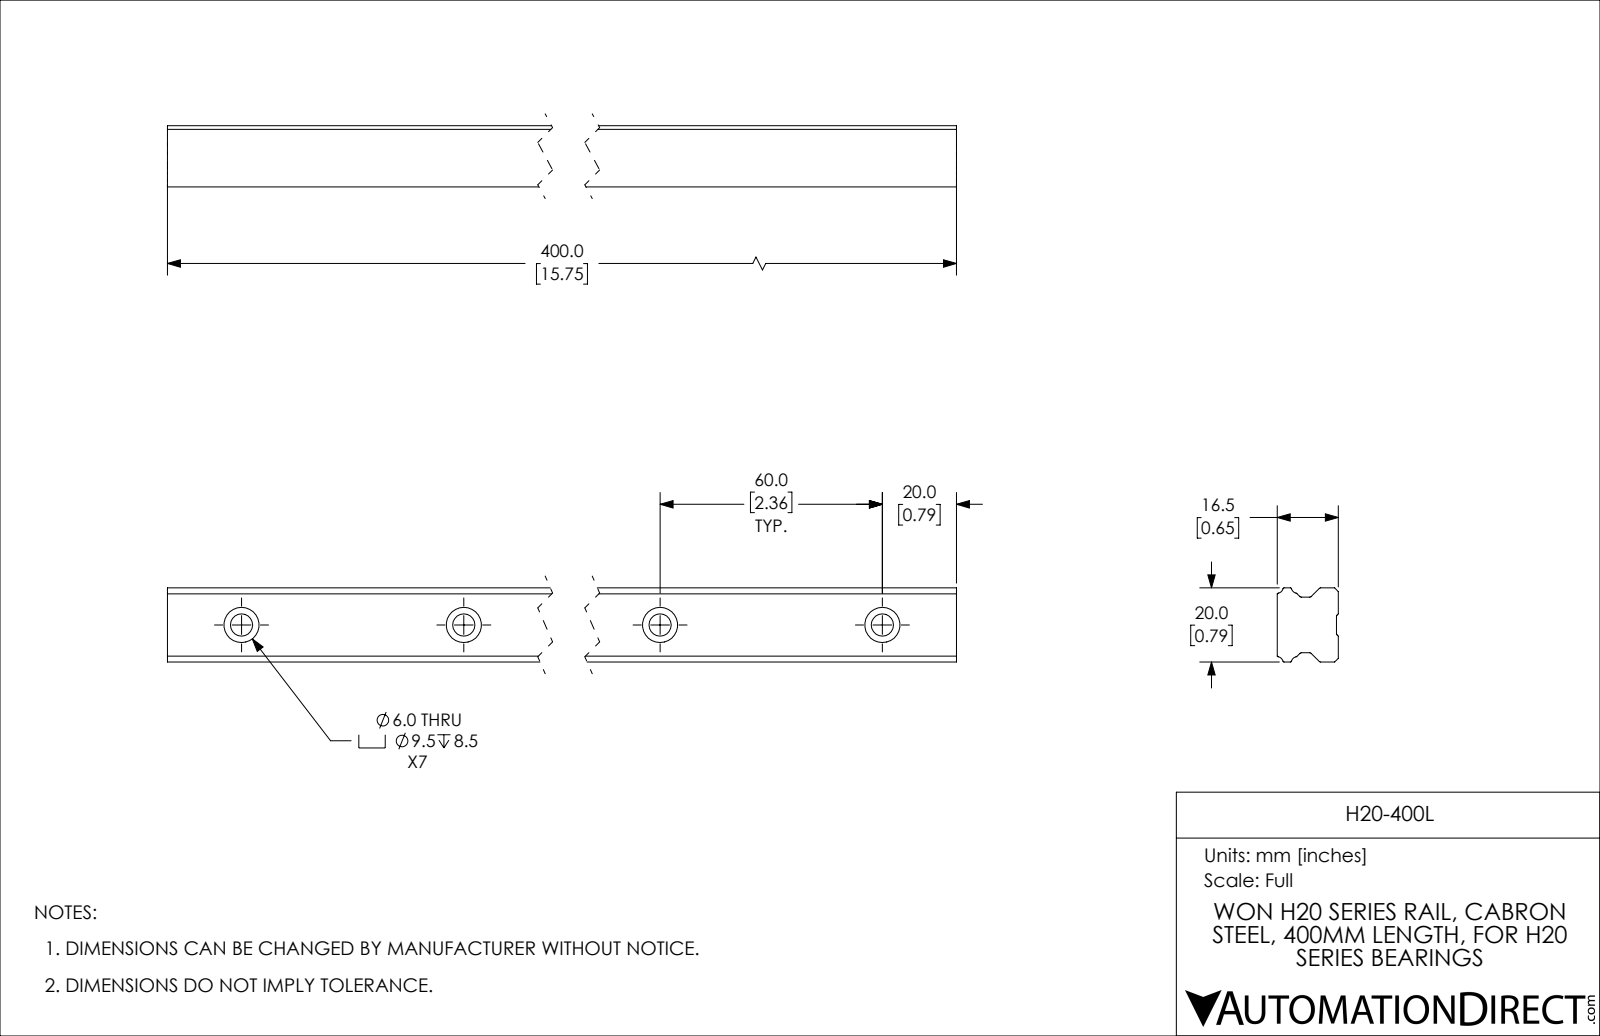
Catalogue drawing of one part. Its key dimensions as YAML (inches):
part_name: "H20-400L"
step_written_by: "SolidWorks 2019 (CONFIG_CONTROL_DESIGN)"
units: inches
bodies: {solids: 1, faces: 110, planar: 48, cylindrical: 62, other: 0}
overall_size: [15.748, 0.787, 0.65]
volume: 6.87
surface_area: 50.88
round_holes:
  - {diameter: 0.236, count: 7}
  - {diameter: 0.374, count: 7}
partial_cylinders:
  - {radius: 0.02, count: 12}
  - {radius: 0.012, count: 4}
  - {radius: 0.063, count: 4}
face_to_face_distances: [0.65, 0.787, 0.098, 0.689, 0.02, 0.63, 0.326, 0.591, 0.334, 0.668]
hole_center_spacings: [2.362, 4.724, 7.087, 9.449, 11.811, 14.173]
